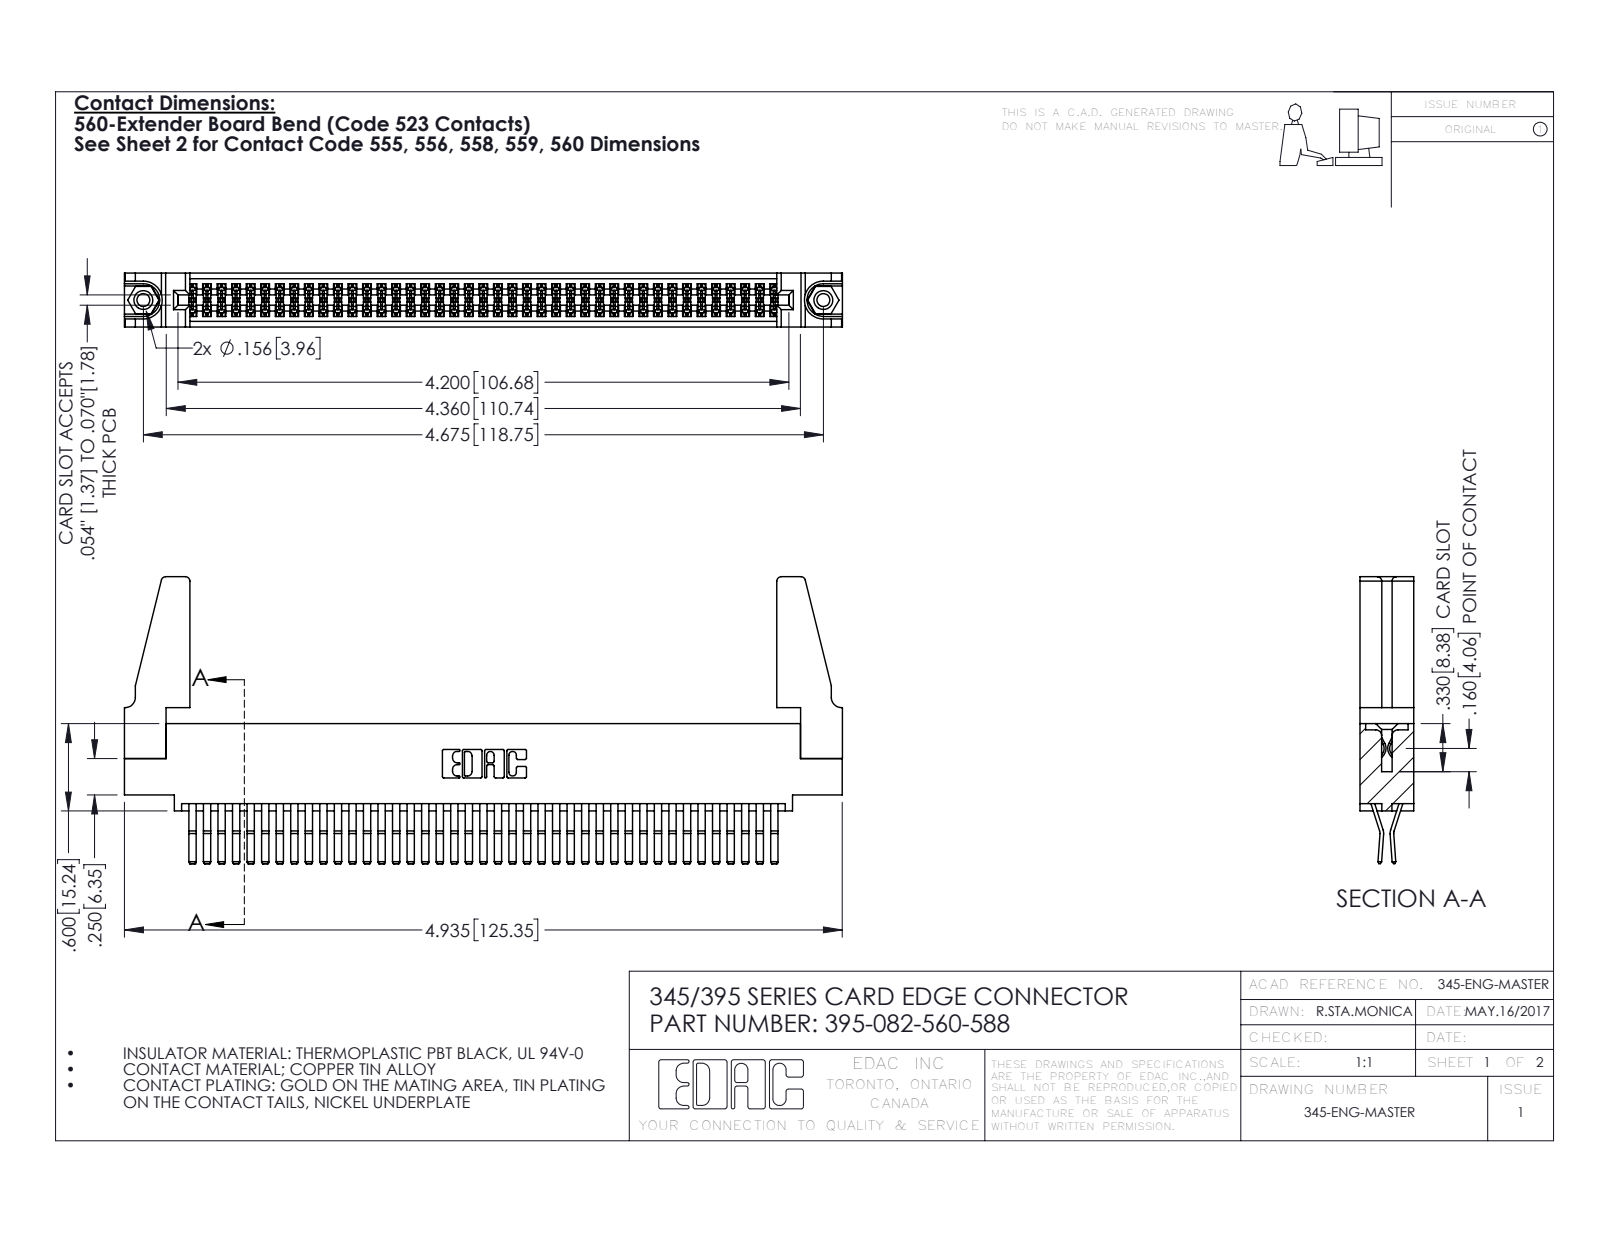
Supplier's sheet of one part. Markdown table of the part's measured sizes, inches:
| quantity | value |
| --- | --- |
| part name | 345 Part_0.110 Offset - 0.156 Dia-TH; 345-250-001_345-250-001-102; 345-220-078_345-220-088; 395-082-560-588 (+1 more) |
| STEP written by | SolidWorks 2016 (CONFIG_CONTROL_DESIGN) |
| units | inches |
| bodies | 87 solids, 4518 faces (2862 planar, 1640 cylindrical, 16 other) |
| overall size | 4.936 × 1.972 × 0.37 |
| volume | 0.969 in³ |
| surface area | 36.04 in² |
| round holes (diameter × count) | 0.089 × 2, 0.125 × 2, 0.156 × 2, 0.064 × 1 |
| round bosses / shafts (diameter × count) | 0.155 × 2 |
| partial cylindrical surfaces (radius × count) | 0.006 × 124, 0.01 × 22, 0.03 × 8, 0.007 × 6, 0.031 × 6, 0.026 × 3, 0.01 × 2, 0.014 × 2 |
| main face-to-face distances | 0.072, 0.298, 0.025, 0.37, 0.2, 0.098, 0.272, 0.225, 0.175, 0.149 |
| hole center spacings | 0.27, 4.439, 4.675 |
